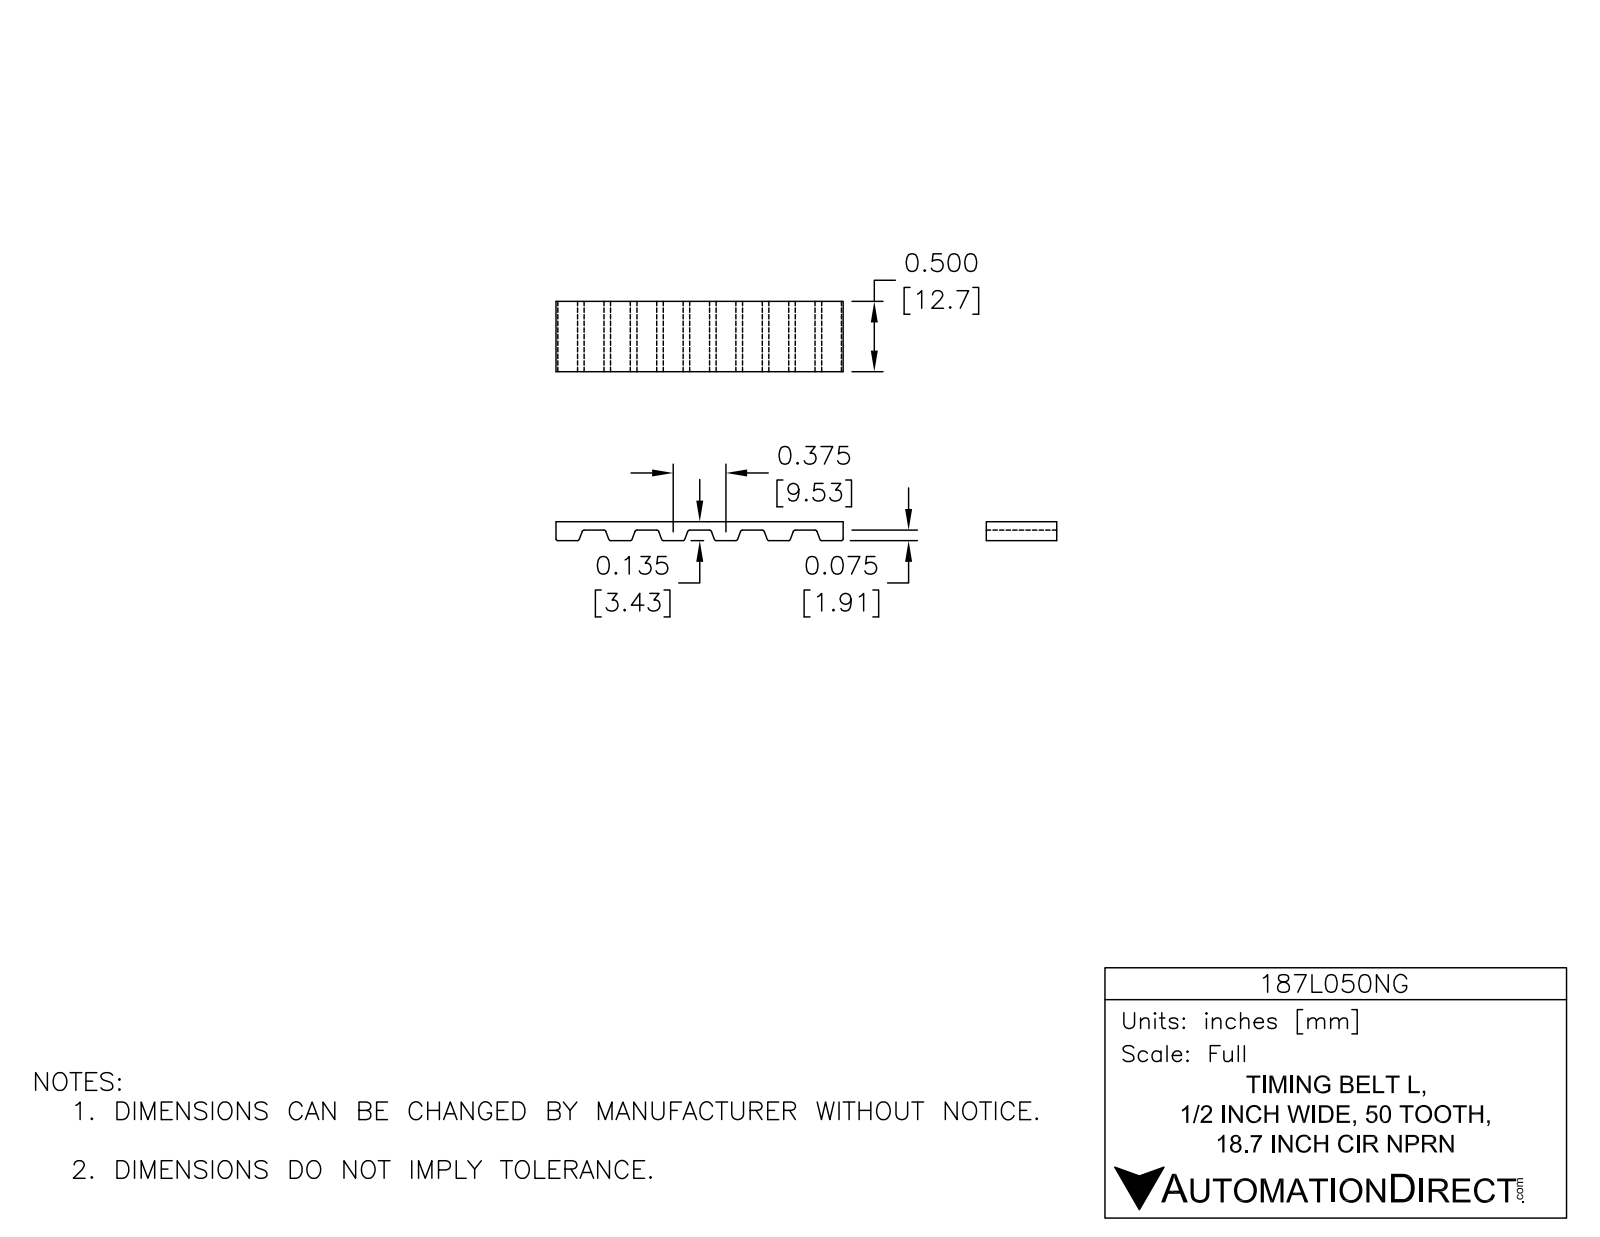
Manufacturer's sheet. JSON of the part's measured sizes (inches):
{"part_name": "187L050NG", "step_written_by": "SolidWorks 2014 (AUTOMOTIVE_DESIGN)", "units": "inches", "bodies": {"solids": 1, "faces": 417, "planar": 176, "cylindrical": 241, "other": 0}, "overall_size": [7.663, 3, 0.5], "volume_in3": 0.842, "surface_area_in2": 24.13, "partial_cylinders_radius": [[0.02, 196], [1.435, 2], [1.5, 2]], "face_to_face_distances": [0.065, 2.935, 3, 0.5, 2.87, 0.14, 2.86, 0.075, 2.795, 0.352]}
